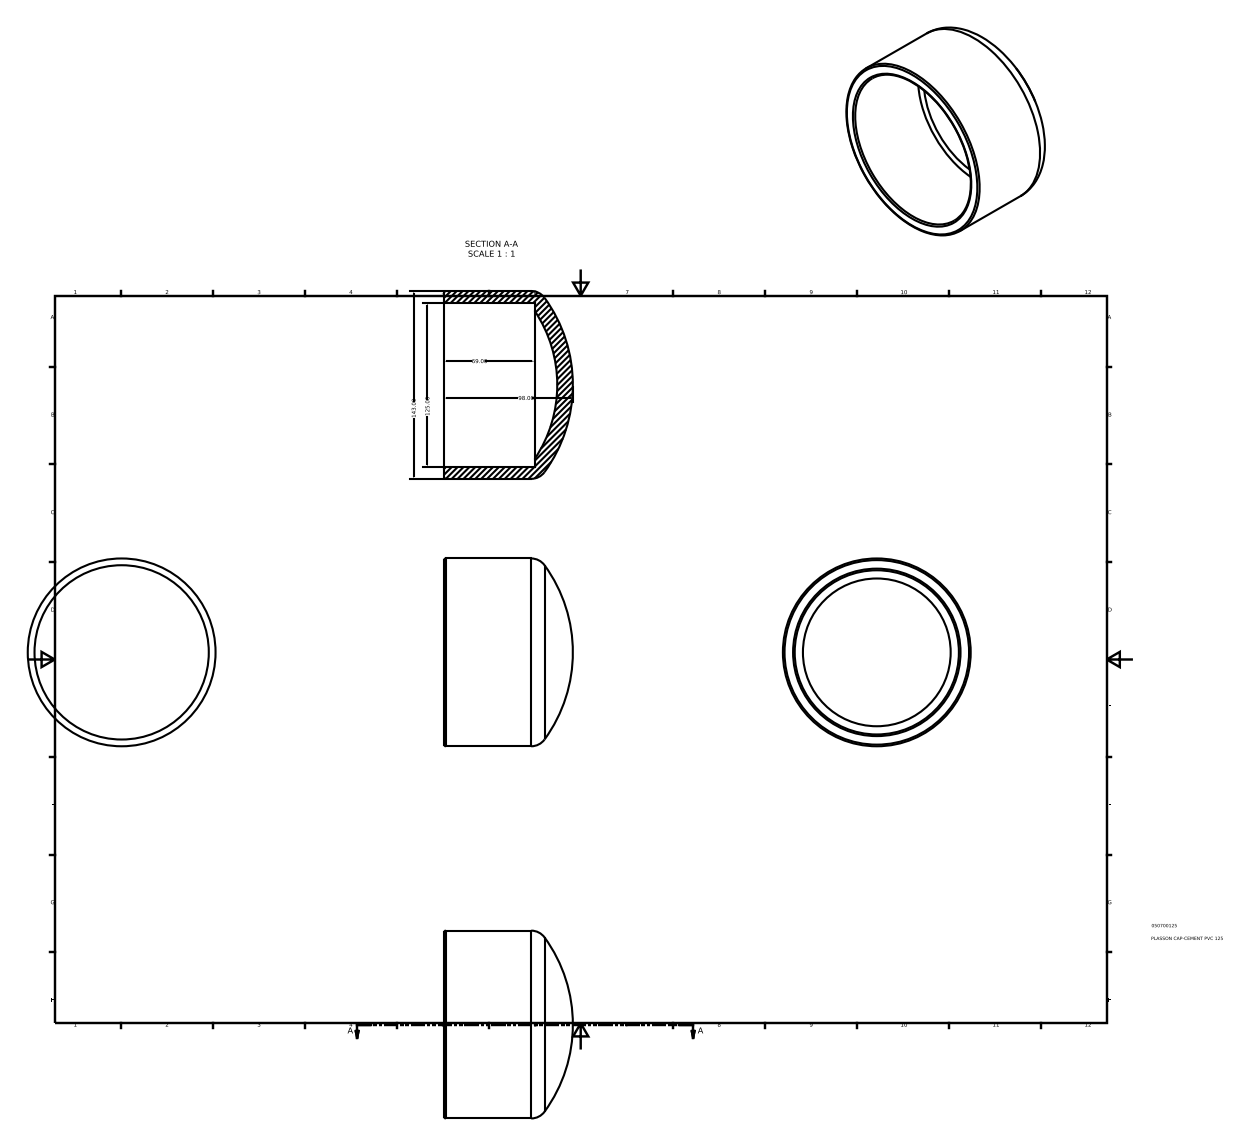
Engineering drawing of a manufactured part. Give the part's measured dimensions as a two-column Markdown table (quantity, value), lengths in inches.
| quantity | value |
| --- | --- |
| part name | 050700125 |
| STEP written by | Autodesk Inventor 2015 (AUTOMOTIVE_DESIGN) |
| units | inches |
| bodies | 1 solid, 9 faces (2 planar, 2 cylindrical, 5 other) |
| overall size | 5.63 × 5.63 × 3.858 |
| volume | 26.86 in³ |
| surface area | 145.5 in² |
| round holes (diameter × count) | 4.921 × 1 |
| round bosses / shafts (diameter × count) | 5.63 × 1 |
| main face-to-face distances | 2.717 |
